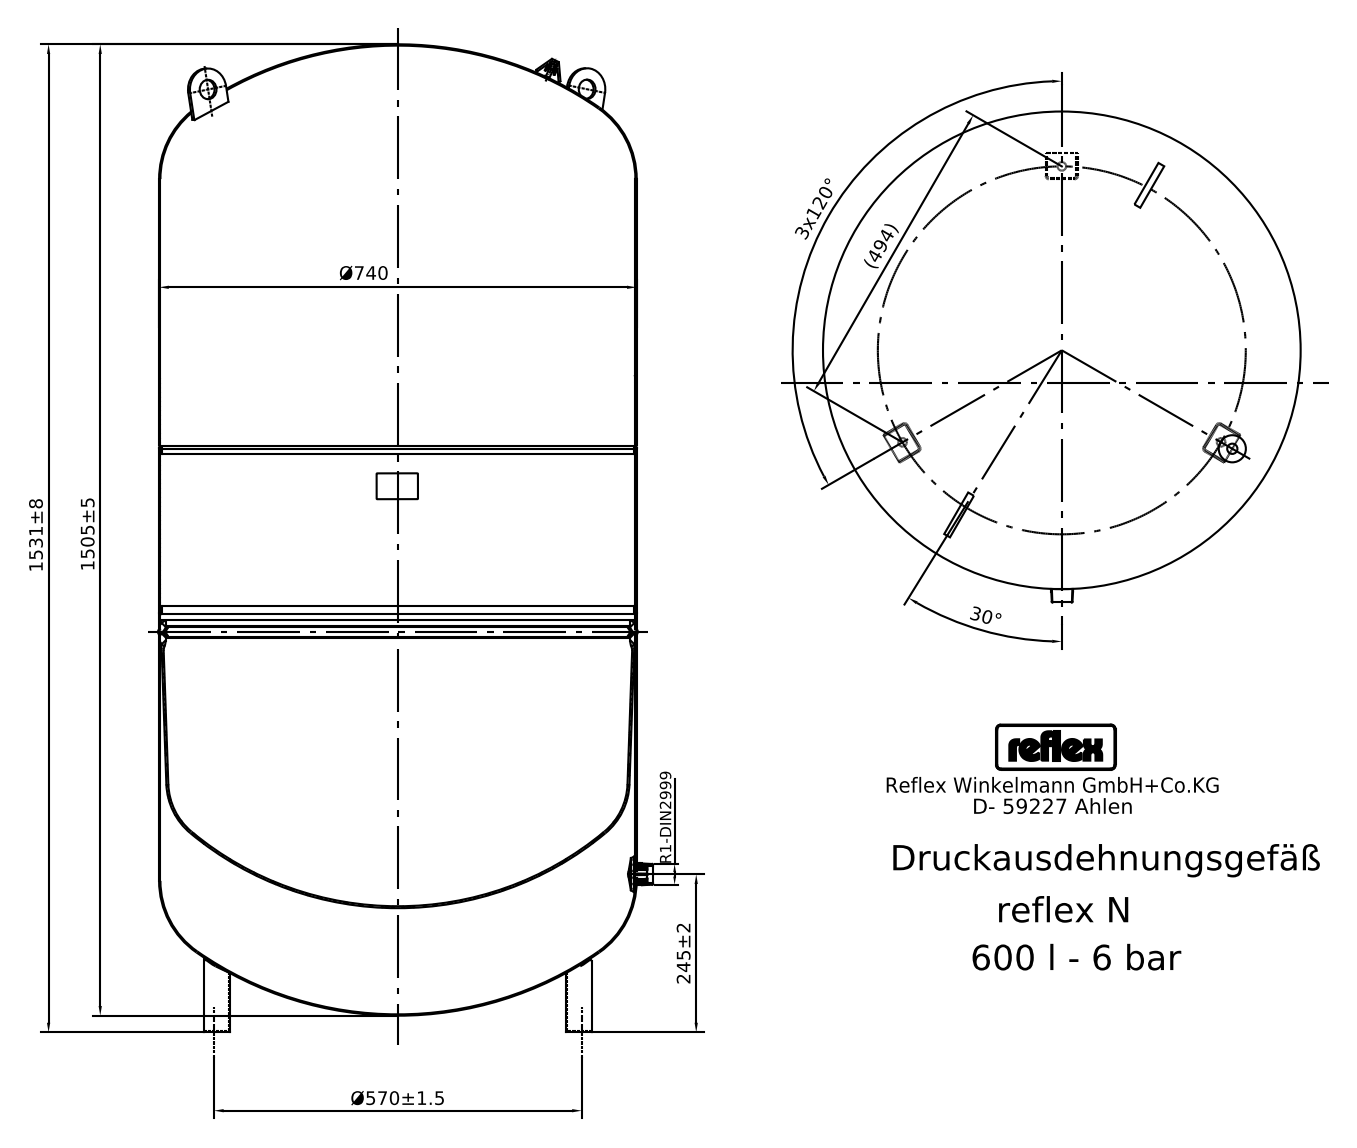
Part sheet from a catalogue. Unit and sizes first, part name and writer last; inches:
Units: inches
Overall size (bounding box): 60.915 × 30.333 × 29.563
Round holes (diameter × count): ⌀0.528 ×3, ⌀0.333 ×1, ⌀1.012 ×1
Round bosses / shafts (diameter × count): ⌀29.134 ×1, ⌀1.327 ×1, ⌀0.404 ×1, ⌀0.213 ×1, ⌀0.142 ×1
Partial cylindrical surfaces — rounded edges, fillets, slot ends (radius × count): R0.039 ×15, R0.098 ×15, R0.197 ×15, R0.155 ×4, R0.062 ×3, R0.106 ×2, R0.186 ×2, R0.256 ×2
Main face-to-face distances: 44.37, 0.098, 1.87, 1.772, 1.969, 16.689, 27.681, 26.807, 10.118, 17.563
Hole centre spacings: 11.22, 19.435
Volume: 36 100 in³ · Surface area: 8 818 in²
Bodies: 16 solids, 255 faces (101 planar, 95 cylindrical, 59 other)
STEP written by: Mechanical Desktop 2008 (CONFIG_CONTROL_DESIGN)
